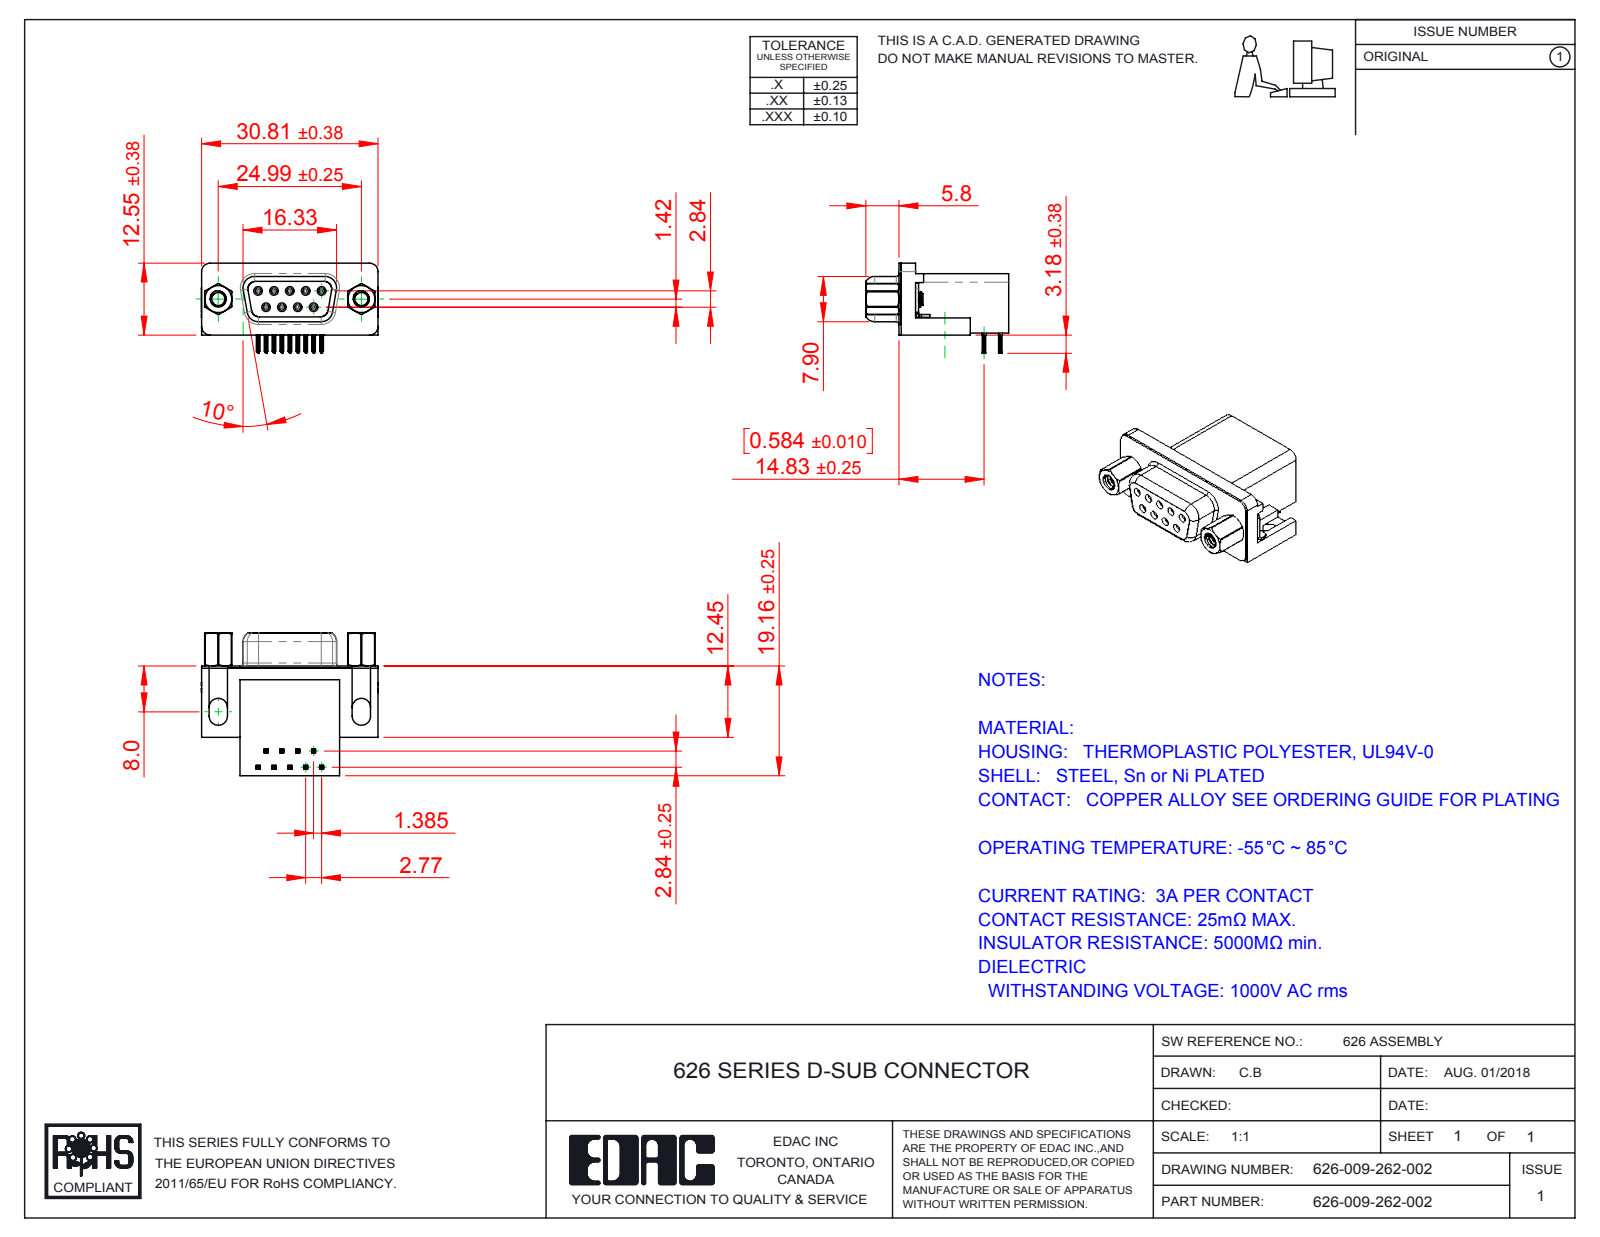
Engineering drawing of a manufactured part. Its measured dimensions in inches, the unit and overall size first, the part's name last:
Units: inches
Overall size (bounding box): 1.216 × 0.983 × 0.619
Round holes (diameter × count): ⌀0.031 ×9, ⌀0.035 ×9, ⌀0.09 ×2, ⌀0.157 ×2, ⌀0.189 ×2, ⌀0.197 ×2
Round bosses / shafts (diameter × count): ⌀0.047 ×9, ⌀0.193 ×2, ⌀0.11 ×2
Partial cylindrical surfaces — rounded edges, fillets, slot ends (radius × count): R0.004 ×72, R0.006 ×36, R0.014 ×18, R0.039 ×18, R0.013 ×9, R0.053 ×8, R0.063 ×8, R0.059 ×7
Main face-to-face distances: 0.016, 0.407, 0.739, 0.754, 0.64, 0.114, 0.014, 0.098, 0.244, 0.421
Hole centre spacings: 0.124, 0.109, 0.218, 0.198, 0.198, 0.327, 0.294, 0.295
Volume: 0.31 in³ · Surface area: 9.019 in²
Bodies: 15 solids, 1608 faces (692 planar, 446 cylindrical, 470 other)
Part name (STEP PRODUCT): 626 Non Board Mount; 626 Housing_9 Socket; 626-009-262-002; 626 Shell_9 Socket (+3 more)
STEP written by: SolidWorks 2016 (CONFIG_CONTROL_DESIGN)
